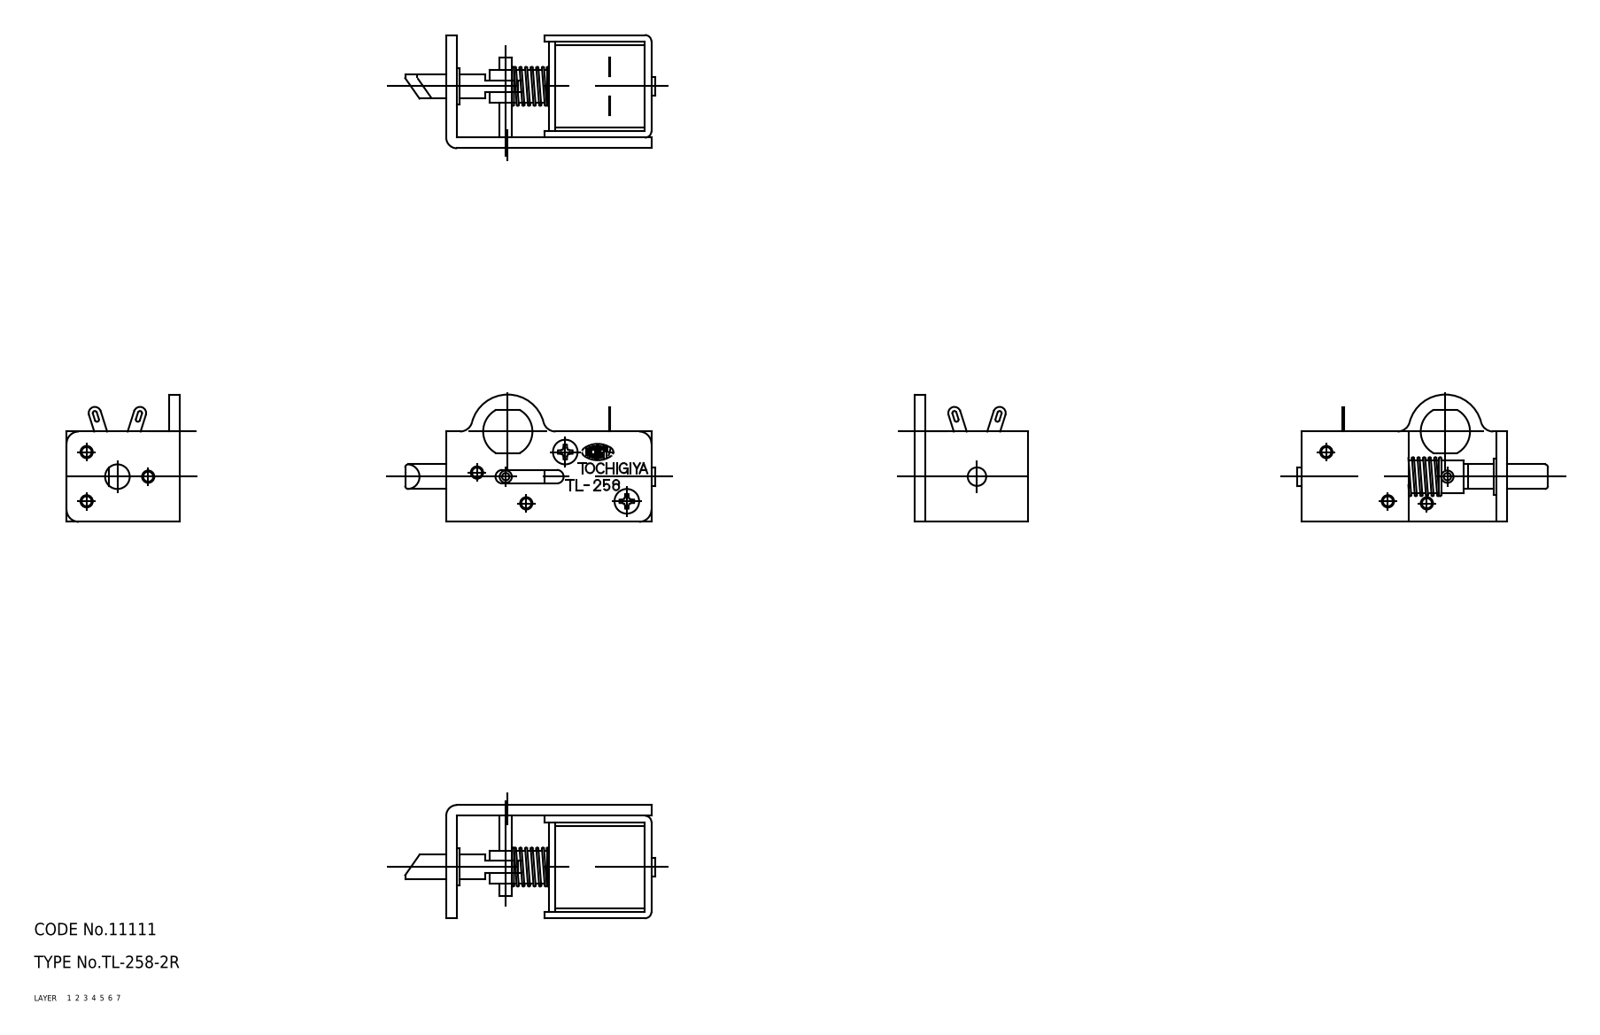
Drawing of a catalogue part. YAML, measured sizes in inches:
part_name: "pin; latch; base; screw_1 (+5 more)"
step_written_by: "SolidWorks 2015 (AUTOMOTIVE_DESIGN)"
units: inches
bodies: {solids: 9, faces: 315, planar: 123, cylindrical: 100, other: 92}
overall_size: [2.402, 1.22, 1.087]
volume: 0.938
surface_area: 18.5
round_holes:
  - {diameter: 0.118, count: 9}
  - {diameter: 0.126, count: 2}
  - {diameter: 0.071, count: 1}
  - {diameter: 0.13, count: 1}
  - {diameter: 0.157, count: 1}
  - {diameter: 0.248, count: 1}
  - {diameter: 0.315, count: 1}
round_bosses_or_shafts:
  - {diameter: 0.236, count: 3}
  - {diameter: 0.787, count: 1}
  - {diameter: 0.177, count: 1}
  - {diameter: 0.118, count: 1}
partial_cylinders:
  - {radius: 0.016, count: 6}
  - {radius: 0.118, count: 6}
  - {radius: 0.02, count: 4}
  - {radius: 0.059, count: 2}
  - {radius: 0.063, count: 2}
  - {radius: 0.065, count: 2}
  - {radius: 0.071, count: 2}
  - {radius: 0.102, count: 1}
face_to_face_distances: [0.921, 0.063, 0.102, 0.984, 0.858, 1.024, 0.945, 0.165, 1.087, 1.866]
hole_center_spacings: [0.472, 0.375, 0.378, 0.591, 0.618, 0.636, 0.756, 1.185]
